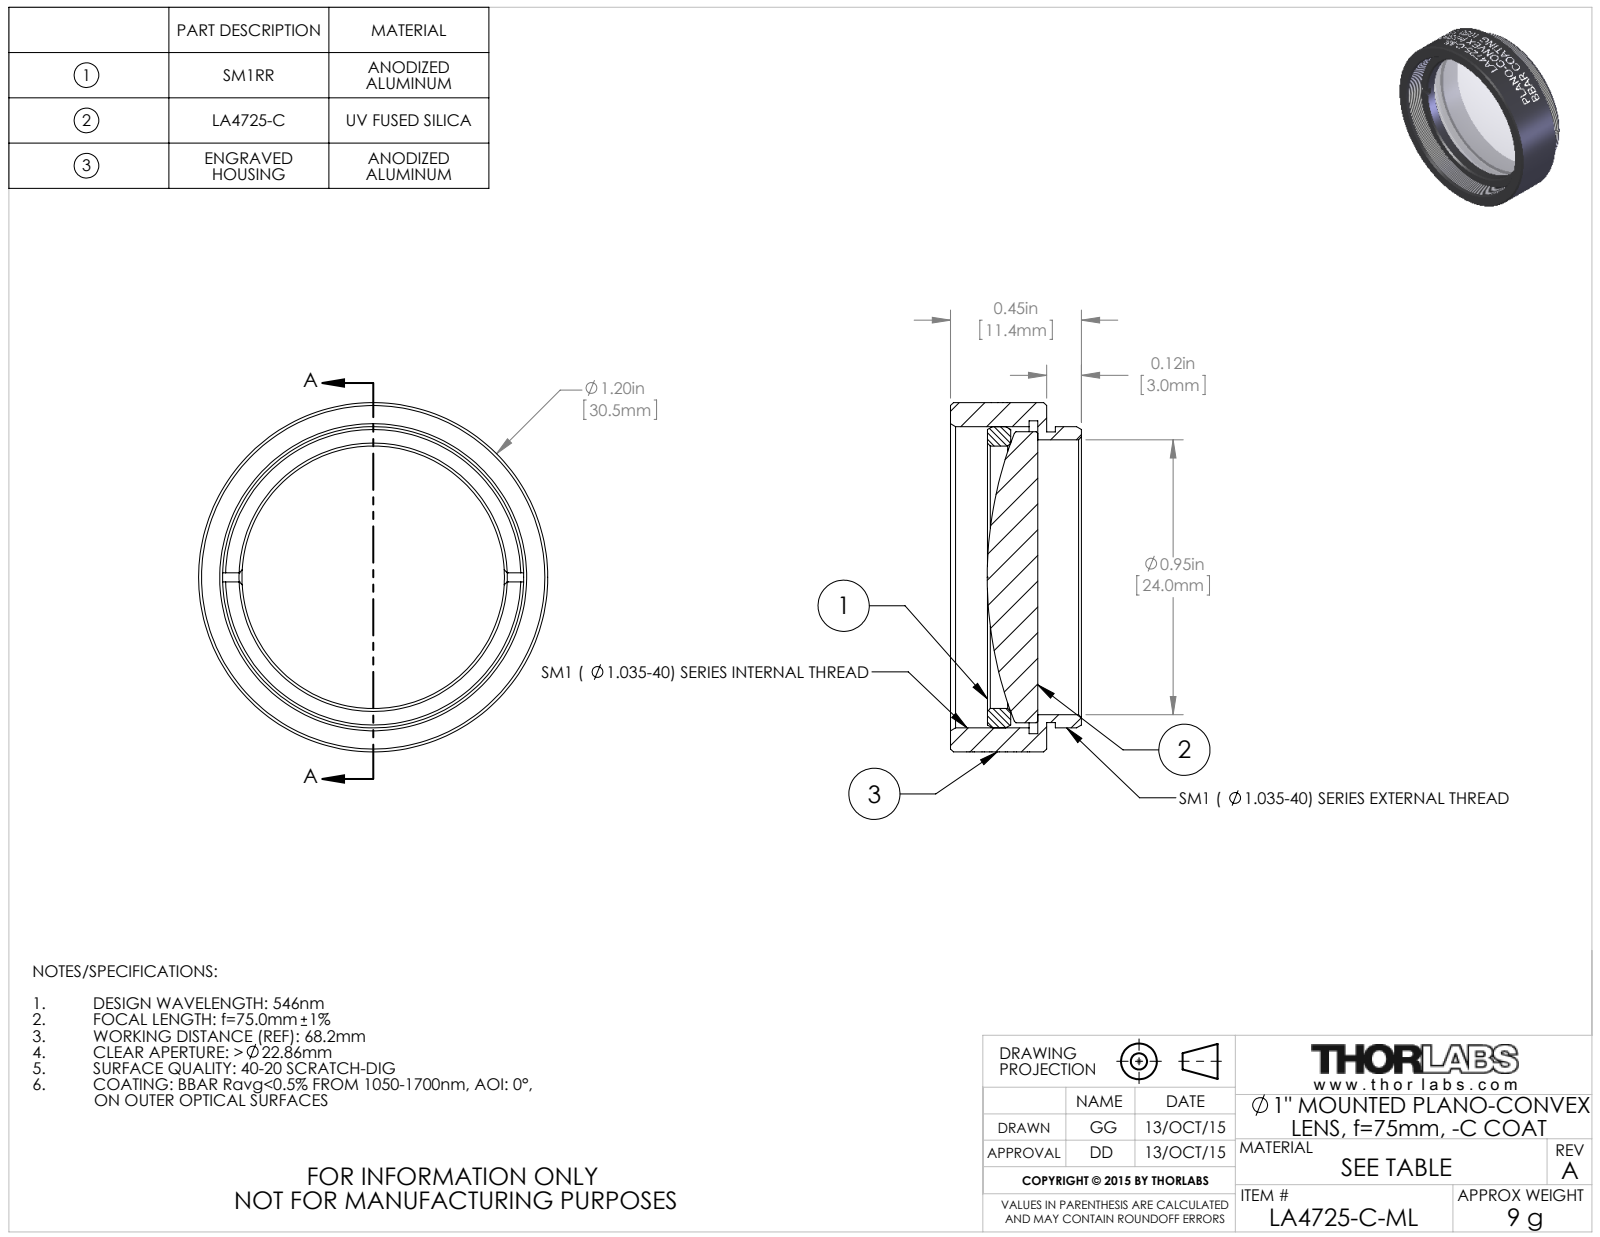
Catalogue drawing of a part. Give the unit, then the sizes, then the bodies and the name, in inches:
Units: inches
Overall size (bounding box): 1.2 × 1.2 × 0.45
Round holes (diameter × count): ⌀0.902 ×1, ⌀0.945 ×1, ⌀1.075 ×1
Round bosses / shafts (diameter × count): ⌀1.2 ×1, ⌀1.035 ×1, ⌀1 ×1, ⌀0.999 ×1
Main face-to-face distances: 0.03, 0.33, 0.3, 0.124, 0.094, 0.206, 0.204, 0.174, 0.08, 0.126
Volume: 0.227 in³ · Surface area: 6.698 in²
Bodies: 3 solids, 161 faces (20 planar, 113 cylindrical, 28 other)
Part name (STEP PRODUCT): TTN039366-E0W
STEP written by: SolidWorks 2014 (CONFIG_CONTROL_DESIGN)
